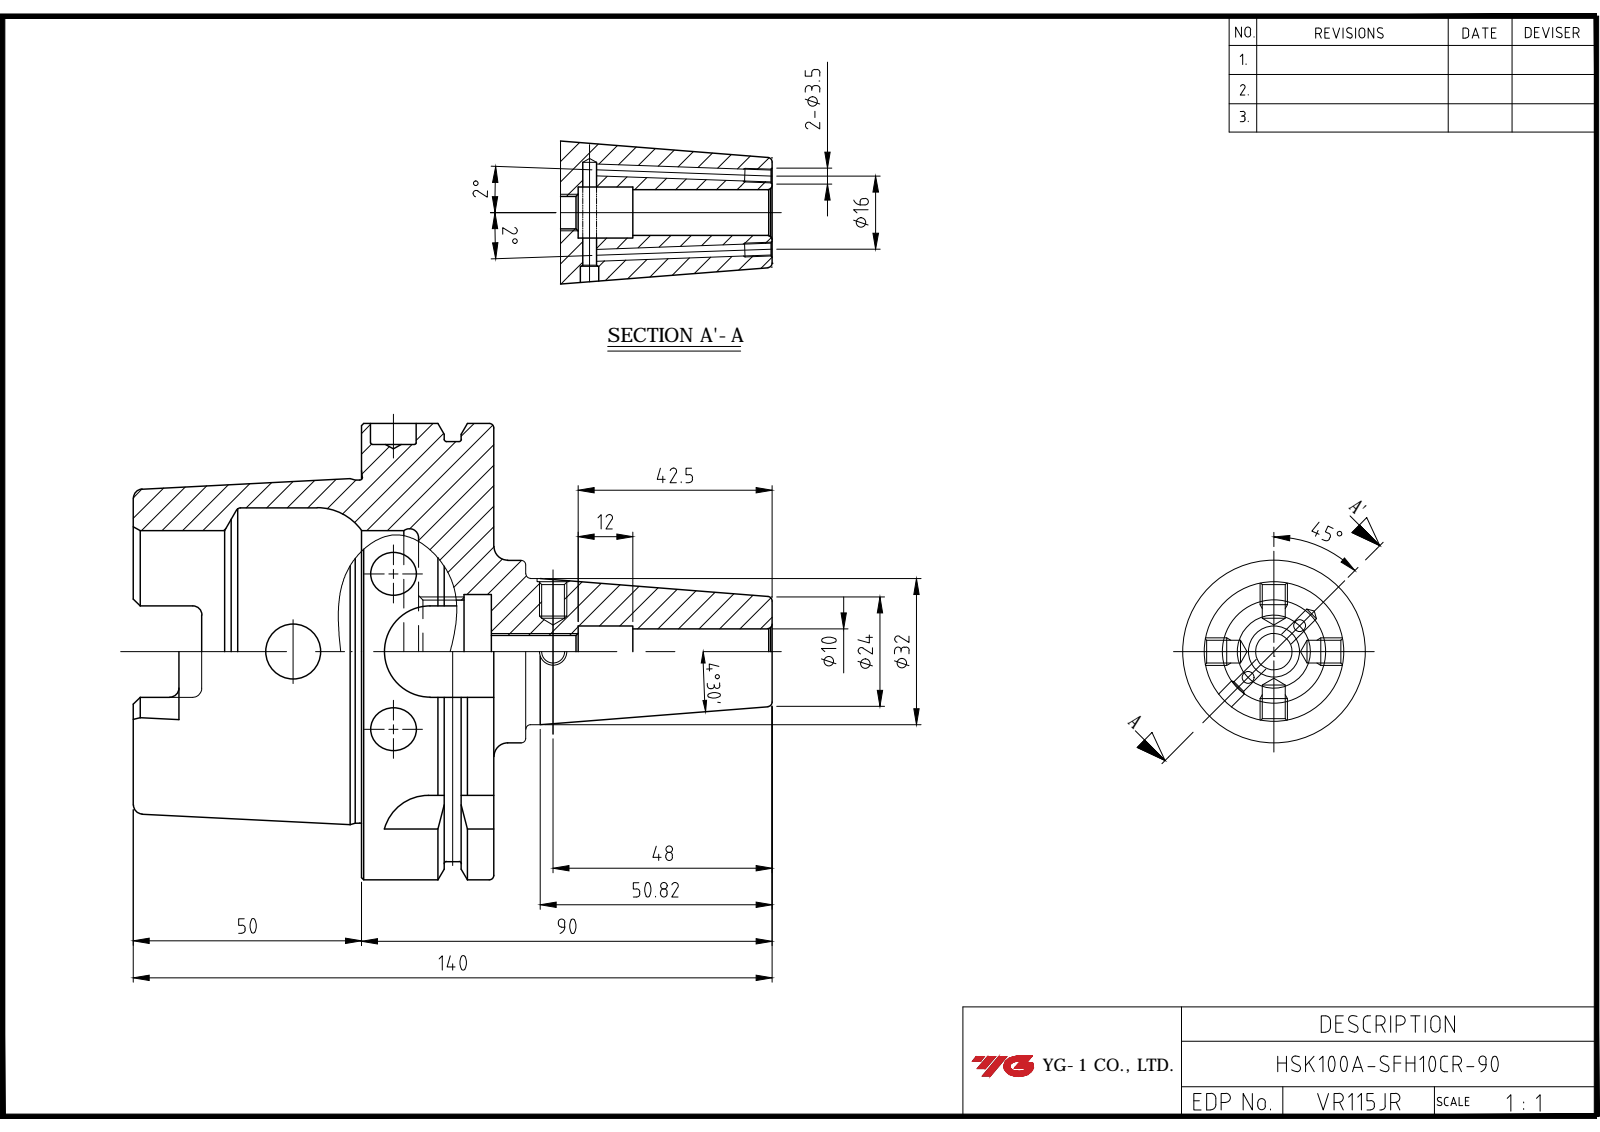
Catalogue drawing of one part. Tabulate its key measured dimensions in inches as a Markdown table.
| quantity | value |
| --- | --- |
| part name | LO-HSK100A-SFH8CR-160 |
| STEP written by | Autodesk Inventor 2024 (AUTOMOTIVE_DESIGN) |
| units | inches |
| bodies | 1 solid, 124 faces (39 planar, 38 cylindrical, 47 other) |
| overall size | 8.268 × 3.937 × 3.937 |
| volume | 19.84 in³ |
| surface area | 99.14 in² |
| round holes (diameter × count) | 0.097 × 2, 0.194 × 1, 0.315 × 1, 0.362 × 1, 0.394 × 1, 0.472 × 1, 0.881 × 1, 0.984 × 1, 2.087 × 1, 2.48 × 1 |
| round bosses / shafts (diameter × count) | 3.937 × 1, 3.622 × 1, 2.969 × 1, 1.575 × 1, 1.063 × 1 |
| partial cylindrical surfaces (radius × count) | 0.079 × 6, 0.192 × 4, 0.394 × 4 |
| main face-to-face distances | 1.142, 0.492, 0.65, 3.11, 2.461, 1.969, 0.394, 3.091, 1.122, 0.63 |
